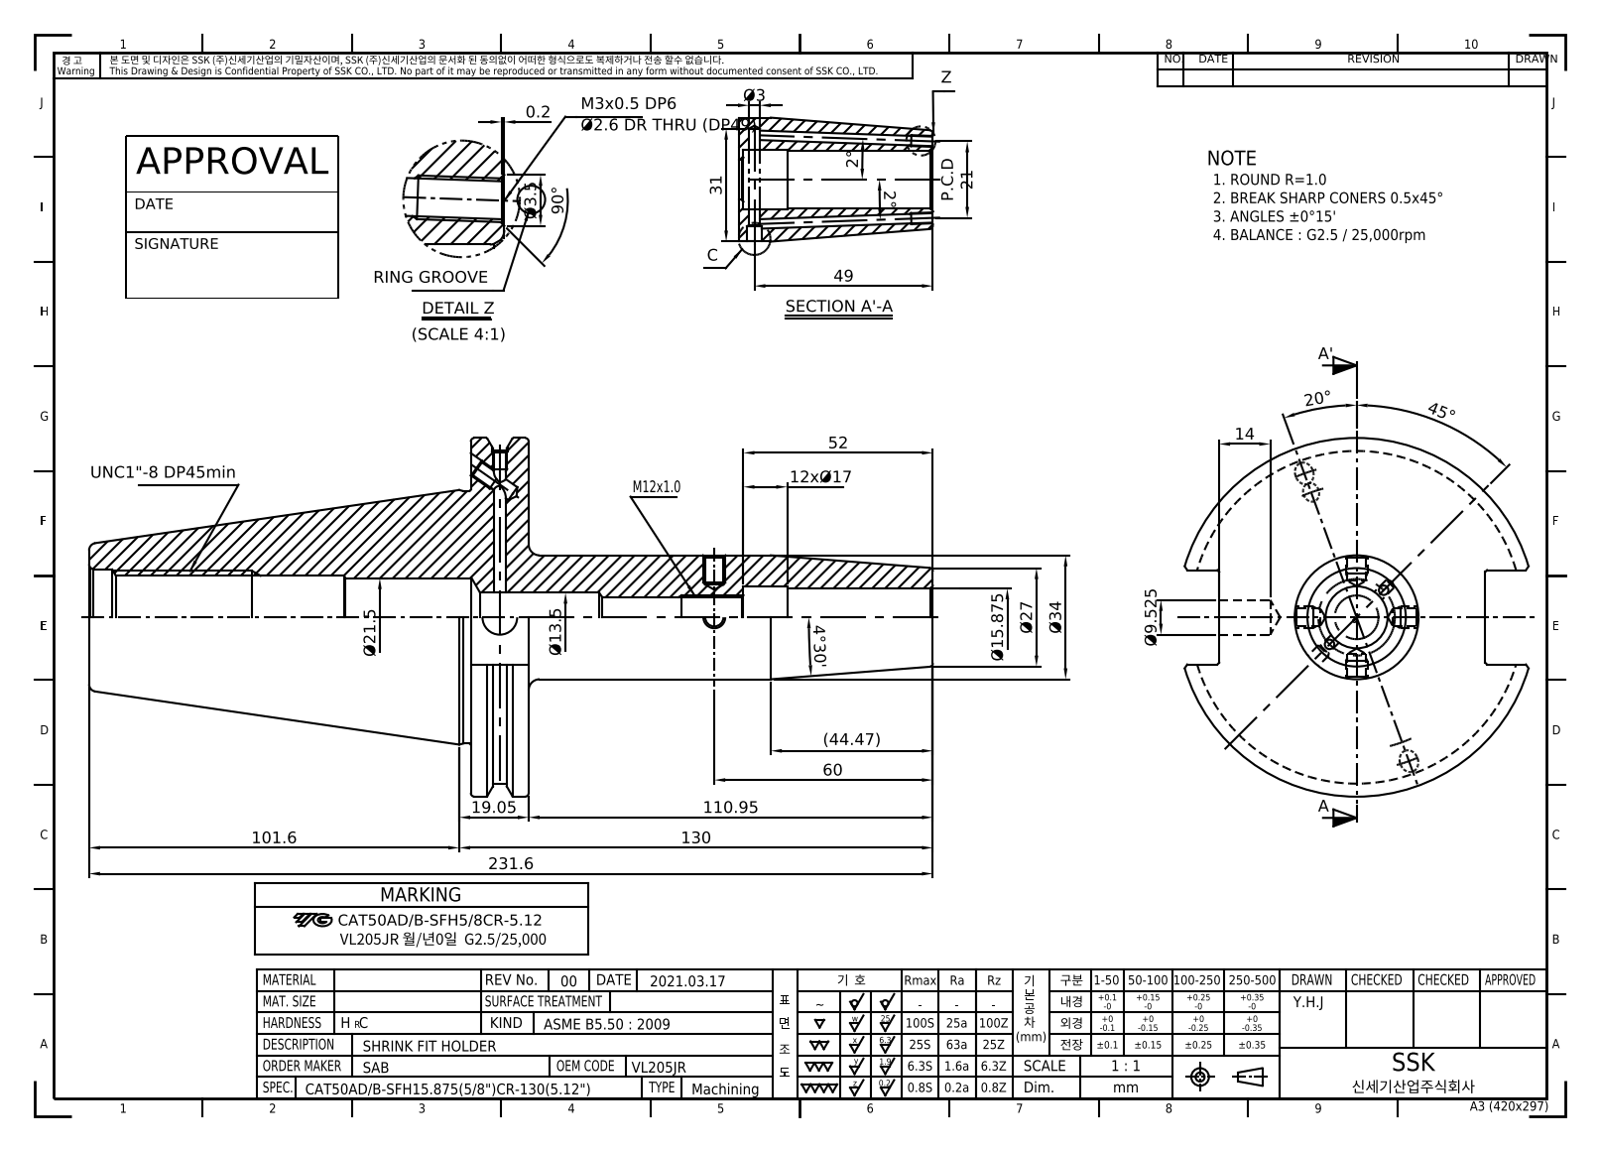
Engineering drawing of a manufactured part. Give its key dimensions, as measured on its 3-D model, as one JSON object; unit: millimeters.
{"part_name": "LO-CAT50ADB-SFH15.875CR-130", "step_written_by": "Autodesk Inventor 2022 (AUTOMOTIVE_DESIGN)", "units": "millimeters", "bodies": {"solids": 1, "faces": 95, "planar": 37, "cylindrical": 33, "other": 25}, "overall_size": [231.6, 98.42, 94.69], "volume_mm3": 397269, "surface_area_mm2": 61350, "round_holes": [[2.46, 2], [3.24, 2], [4.13, 2], [4.2, 2], [5, 2], [3, 1], [4, 1], [9.53, 1], [10.92, 1], [13.5, 1], [15.87, 1], [17, 1]], "round_bosses_or_shafts": [[98.42, 1], [91.29, 1], [69.25, 1], [34, 1]], "face_to_face_distances": [15.88, 104.77, 120.65, 73.03, 25.9, 231.6, 126.83, 110.95, 110.82, 6.05]}
